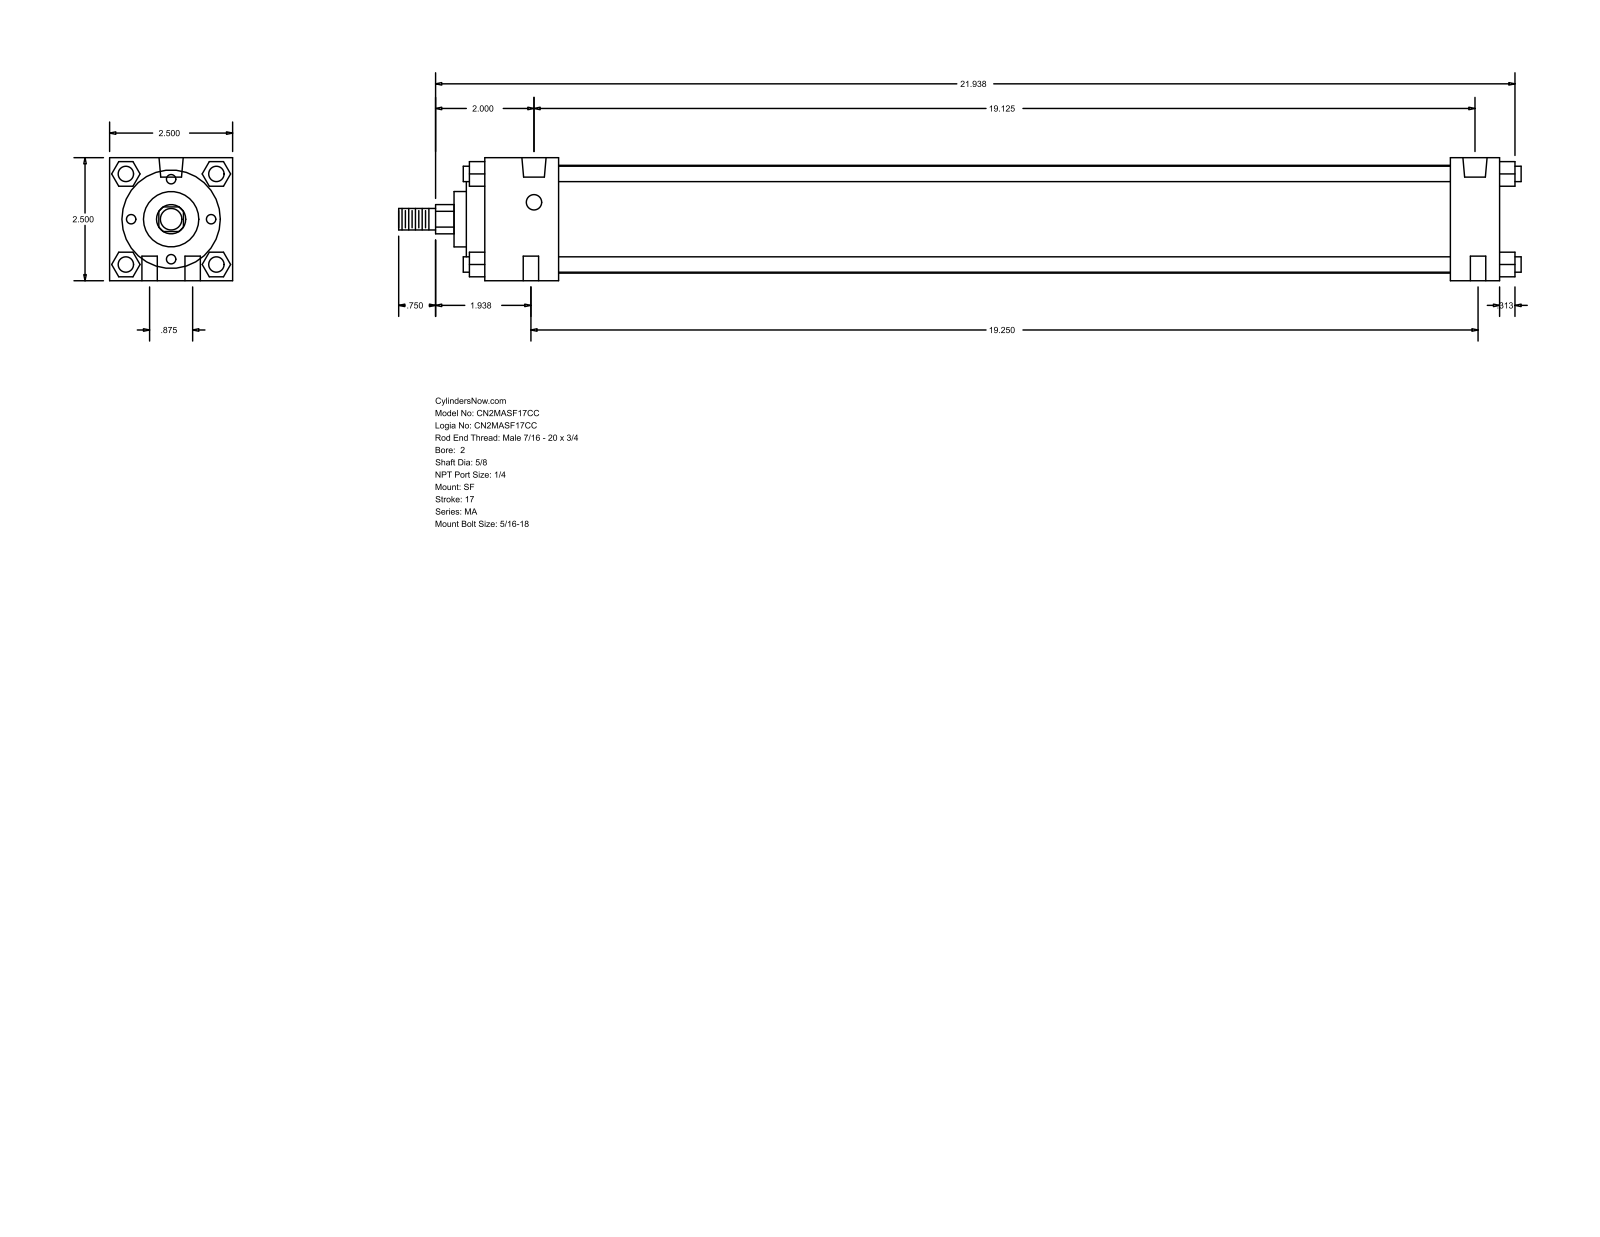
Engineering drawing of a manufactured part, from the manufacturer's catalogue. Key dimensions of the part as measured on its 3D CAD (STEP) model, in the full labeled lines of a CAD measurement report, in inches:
Part name (STEP PRODUCT): MA_SF__0200_0.625
STEP written by: GSSL Pune (CONFIG_CONTROL_DESIGN)
Units: inches
Bodies: 0 solids, 126 faces (95 planar, 31 cylindrical, 0 other)
Overall size (bounding box): 22.813 × 2.5 × 2.5
Round holes (diameter × count): ⌀0.313 ×6, ⌀0.492 ×2
Round bosses / shafts (diameter × count): ⌀0.313 ×4, ⌀2.19 ×1, ⌀2 ×1, ⌀1.125 ×1, ⌀0.625 ×1, ⌀0.437 ×1
Partial cylindrical surfaces — rounded edges, fillets, slot ends (radius × count): R0.297 ×1
Main face-to-face distances: 2.5, 0.5, 1.5, 20.625, 19.625, 1, 18.125, 19.125, 0.375, 1.875
Hole centre spacings: 0.442, 0.875, 19.125, 19.193, 19.193, 19.25, 19.27
